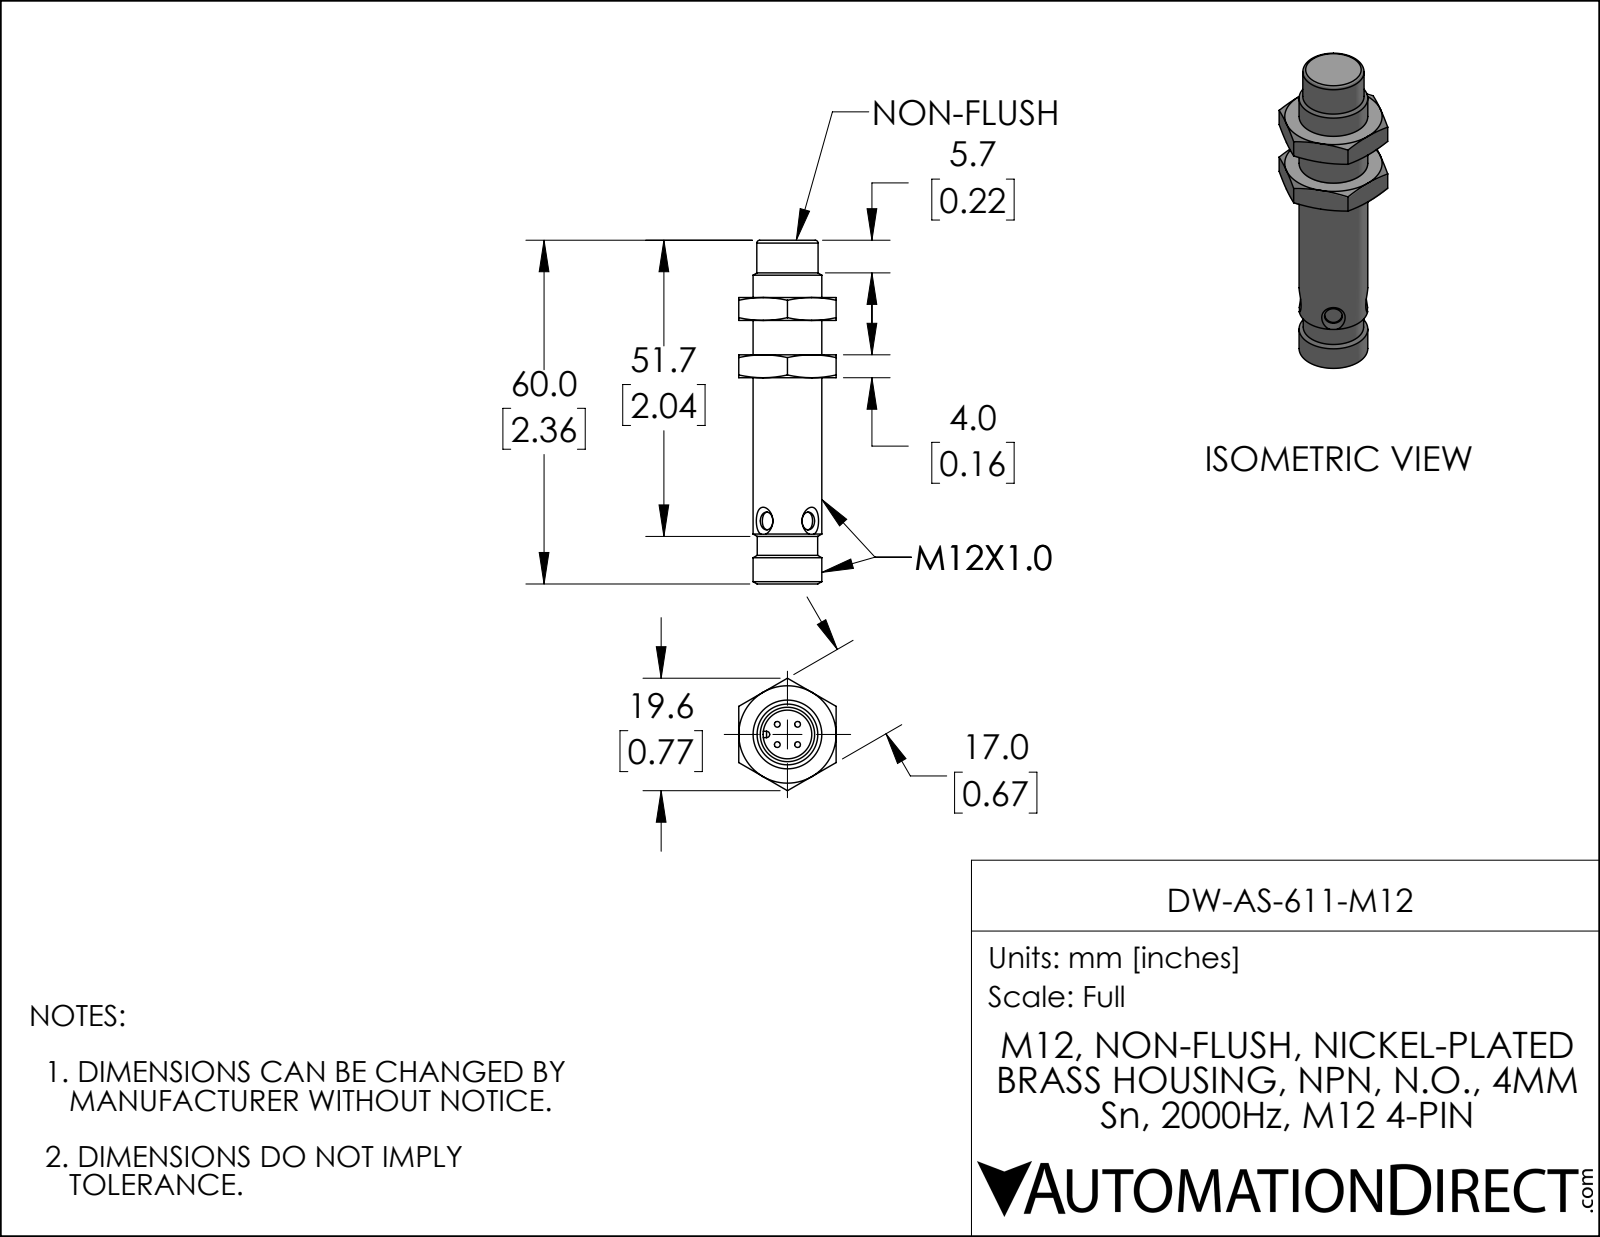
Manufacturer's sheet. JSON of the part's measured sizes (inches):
{"part_name": "DW-AS-611-M12", "step_written_by": "SolidWorks 2019 (AUTOMOTIVE_DESIGN)", "units": "inches", "bodies": {"solids": 1, "faces": 82, "planar": 22, "cylindrical": 21, "other": 39}, "overall_size": [2.362, 0.773, 0.669], "volume_in3": 0.434, "surface_area_in2": 5.407, "round_holes": [[0.122, 2], [0.335, 1]], "round_bosses_or_shafts": [[0.039, 4], [0.472, 1], [0.421, 1], [0.415, 1]], "partial_cylinders_radius": [[0.022, 2], [0.193, 1]], "face_to_face_distances": [0.394, 0.157, 0.669, 0.551, 0.236, 0.787, 0.945, 2.02, 1.626, 1.469]}
